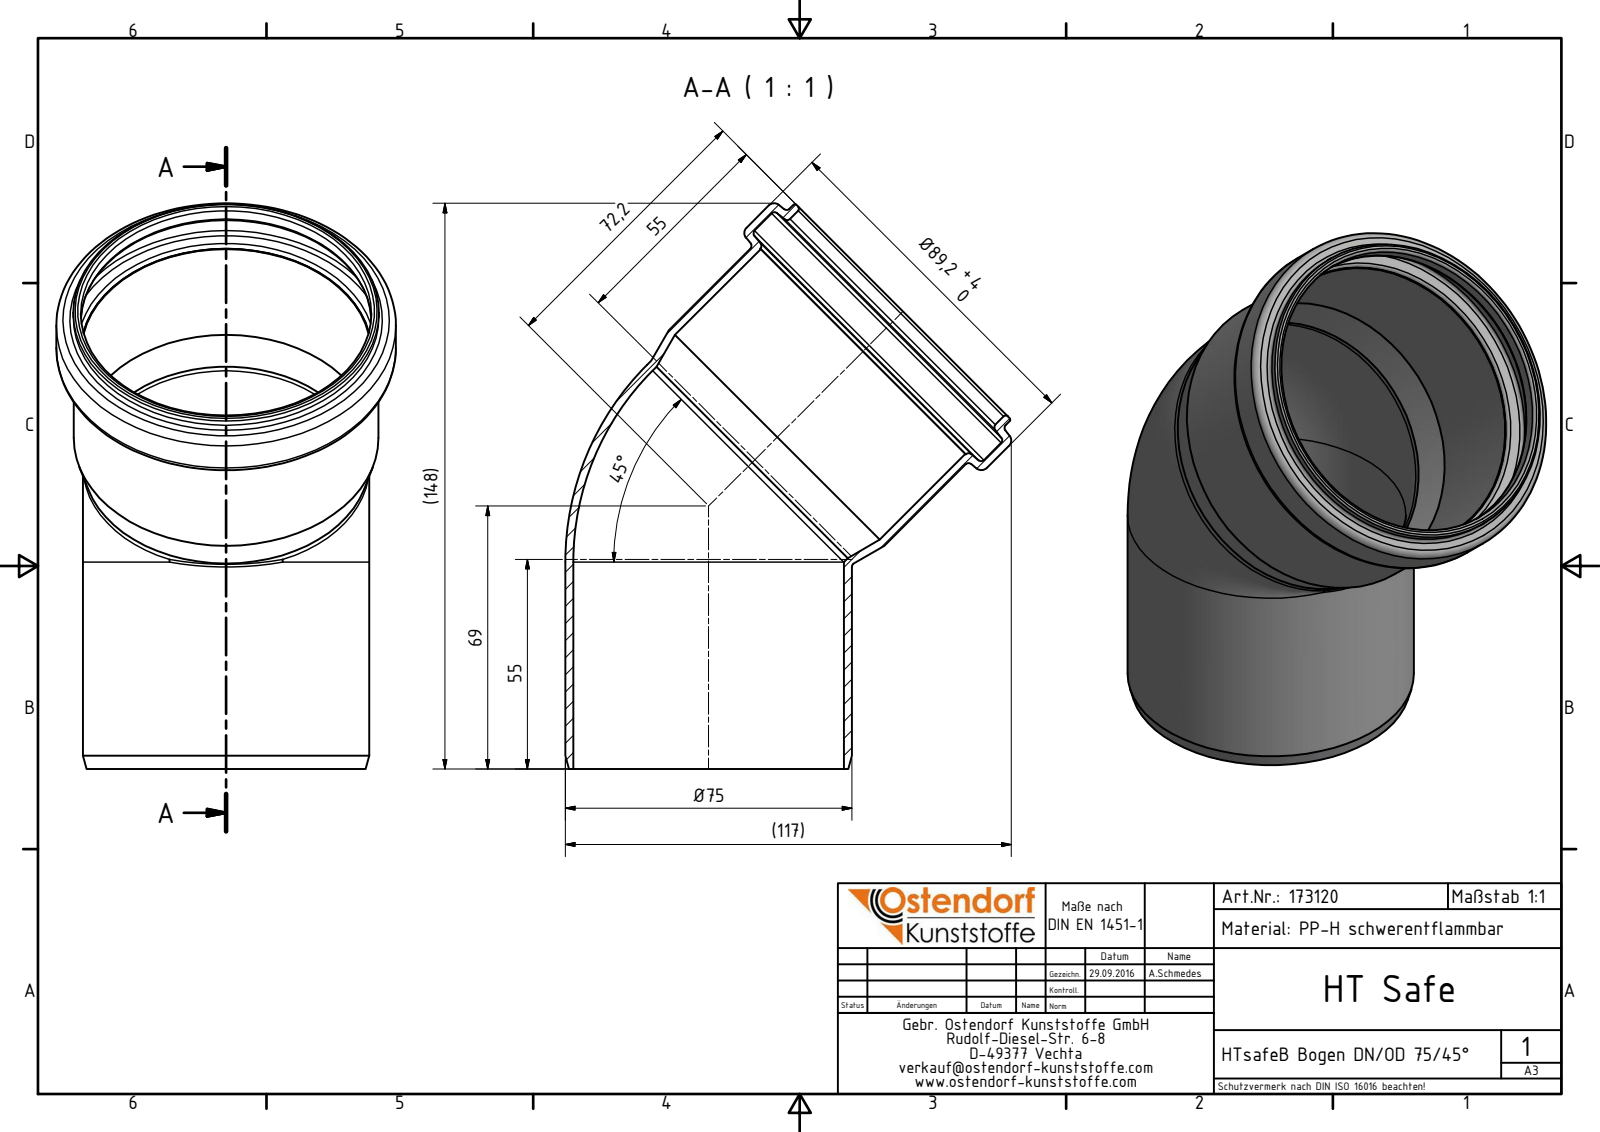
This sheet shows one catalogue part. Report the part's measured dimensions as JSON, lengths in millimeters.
{"part_name": "173120 HTsafeB DN_OD 75_45°", "step_written_by": "Autodesk Inventor 2016 (AUTOMOTIVE_DESIGN)", "units": "millimeters", "bodies": {"solids": 1, "faces": 34, "planar": 3, "cylindrical": 11, "other": 20}, "overall_size": [148.44, 117.04, 89.2], "volume_mm3": 68111, "surface_area_mm2": 70518, "round_holes": [[71, 2], [76.3, 2], [76, 1], [85.2, 1]], "round_bosses_or_shafts": [[75.2, 2], [89.2, 1], [80.3, 1], [80, 1]], "face_to_face_distances": [14.88]}
